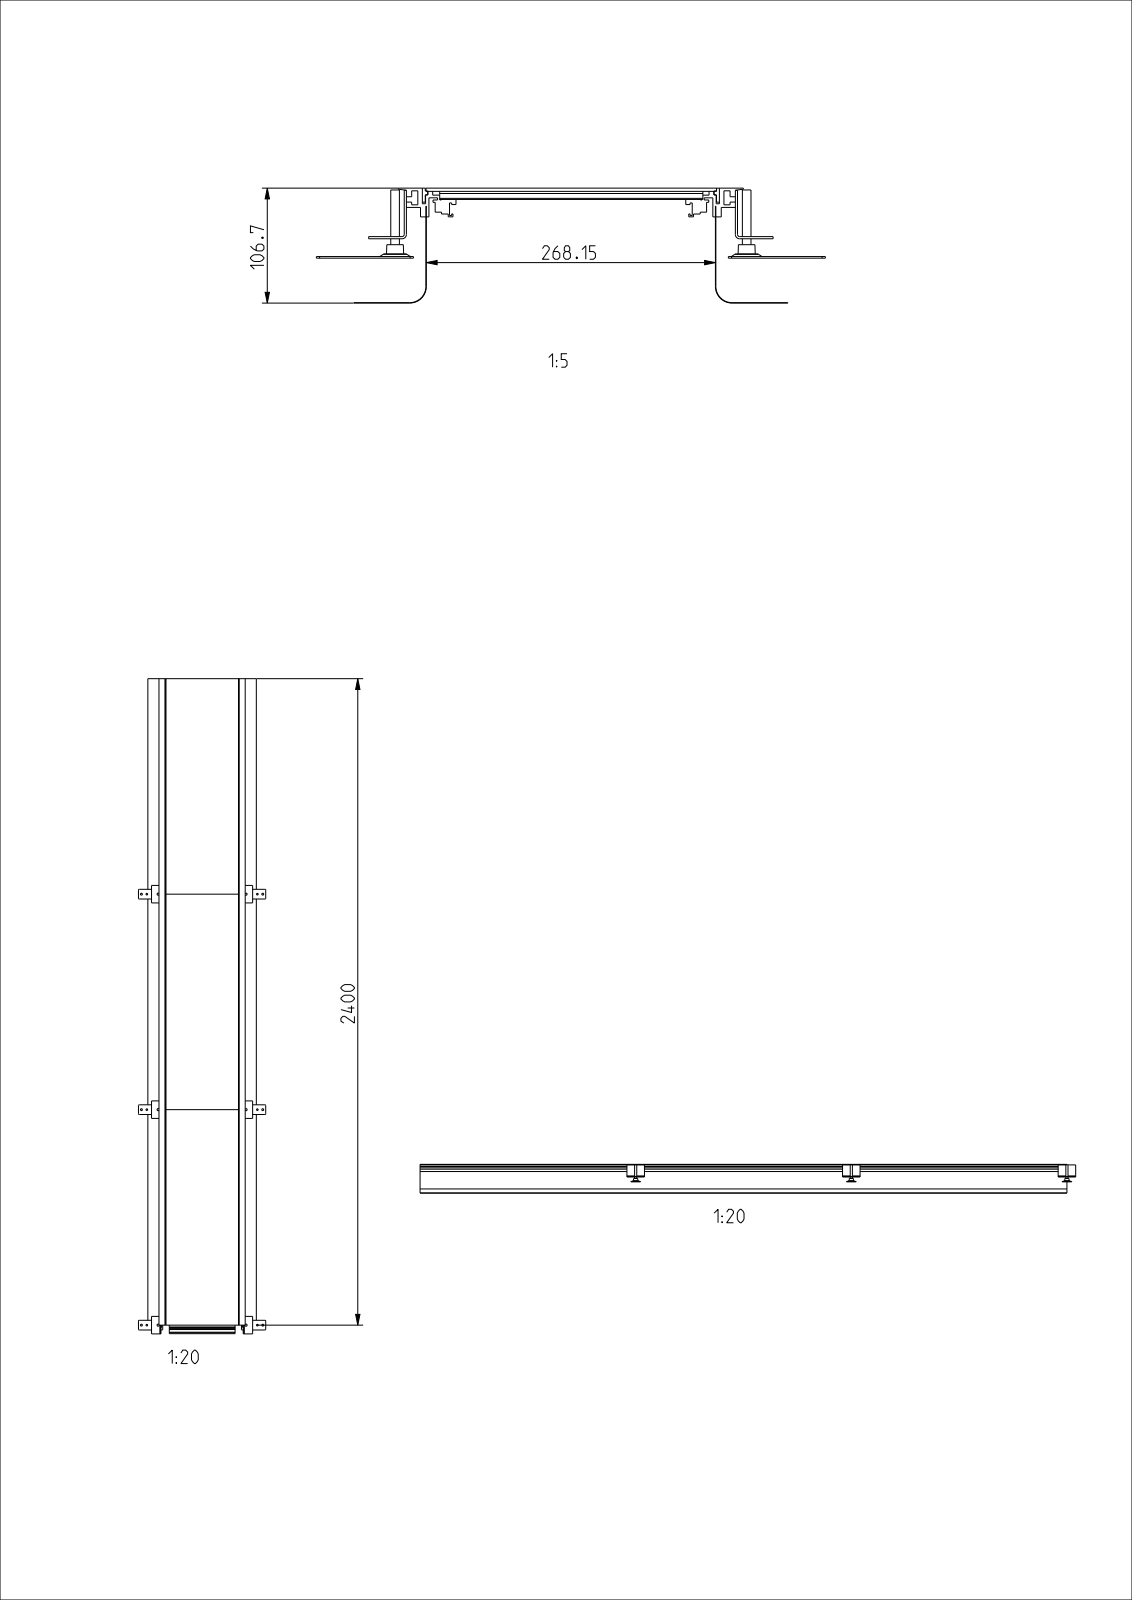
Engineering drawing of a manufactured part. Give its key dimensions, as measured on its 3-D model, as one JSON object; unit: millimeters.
{"part_name": "U05644KUN; U05650KUN; U05985KUN; U05347KUN (+8 more)", "step_written_by": "CREO PARAMETRIC BY PTC INC, 2020281 (AUTOMOTIVE_DESIGN)", "units": "millimeters", "bodies": {"solids": 41, "faces": 720, "planar": 474, "cylindrical": 210, "other": 36}, "overall_size": [2432.5, 472.13, 106.7], "volume_mm3": 5691000, "surface_area_mm2": 4705000, "round_holes": [[6, 6], [7, 6], [8.5, 6], [11.5, 6], [17.5, 6], [23, 6]], "round_bosses_or_shafts": [[20, 6], [8, 6]], "partial_cylinders_radius": [[2, 62], [3, 24], [0.5, 14], [4, 2], [15, 2], [15.4, 2]], "face_to_face_distances": [3, 0.4, 268.55, 103.7, 106.7, 103.3, 106.3, 268.95, 268.15, 6.5], "hole_center_spacings": [800, 800.25, 801.1, 802.4, 880.64, 889.18, 908.3, 20]}
